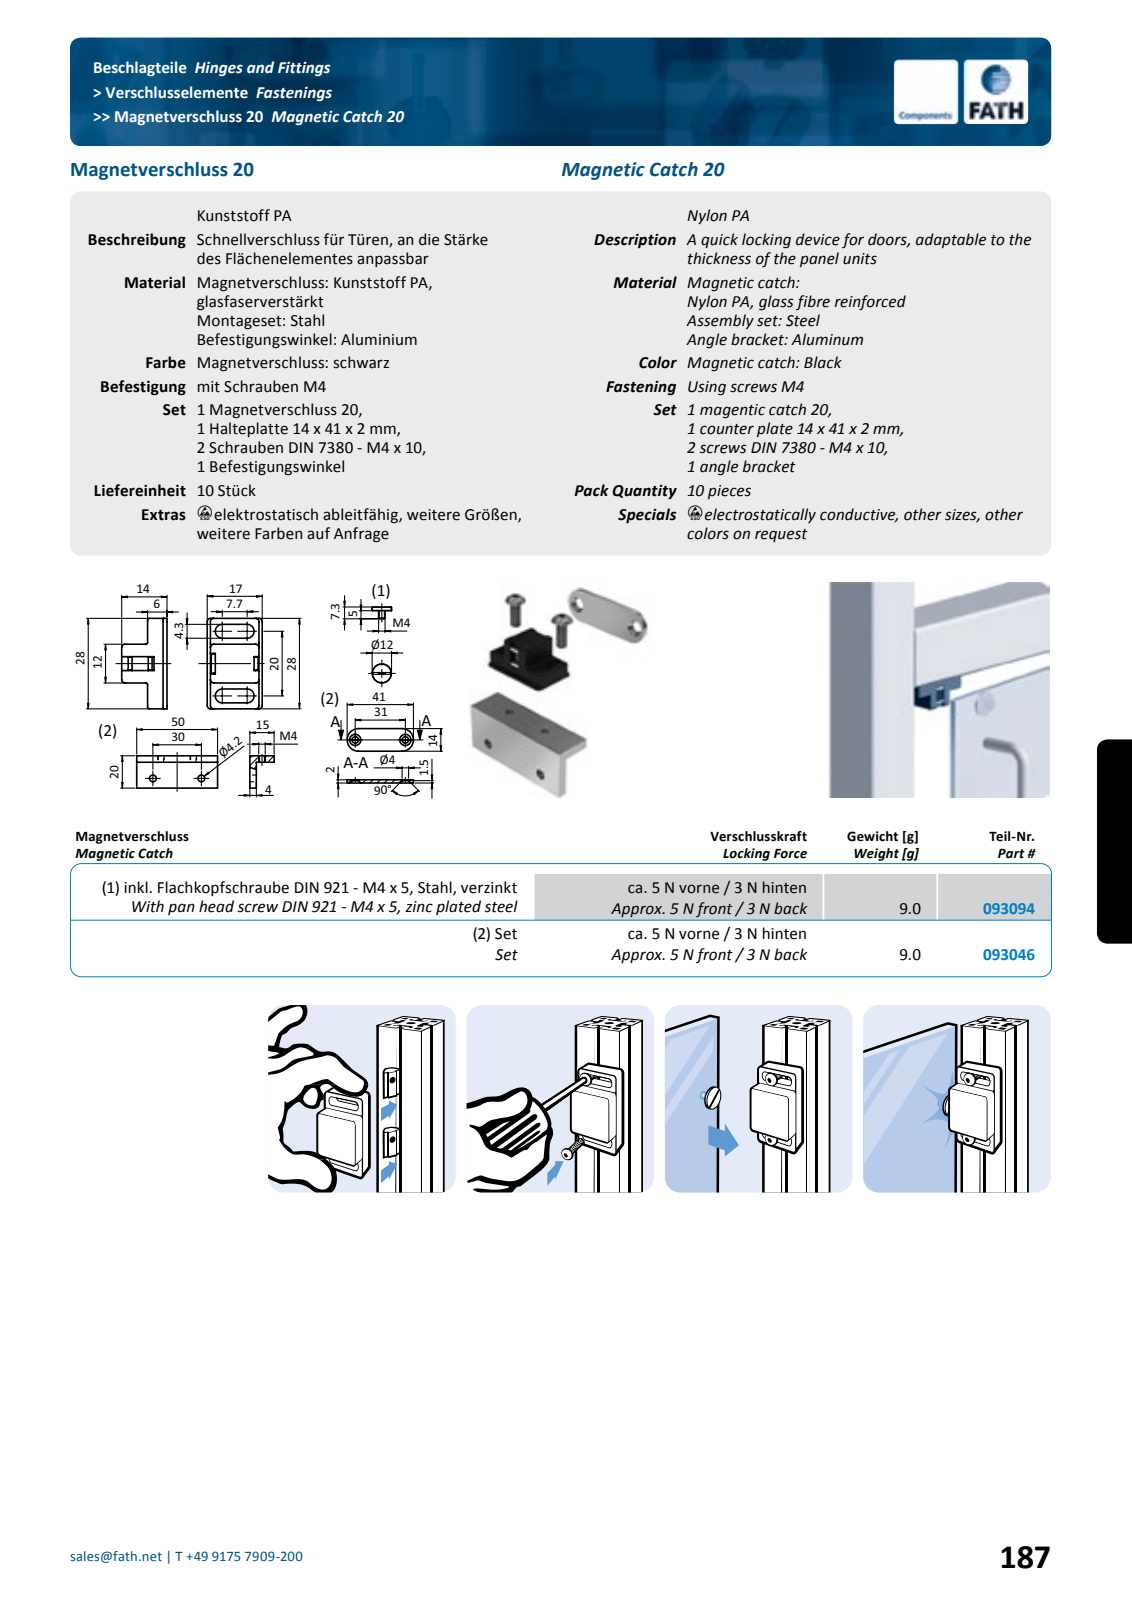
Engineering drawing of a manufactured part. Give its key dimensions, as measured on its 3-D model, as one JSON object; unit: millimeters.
{"part_name": "fath_093046_1; fath_093046_2; fath_093046_3; fath_093046_4 (+4 more)", "step_written_by": "Spatial InterOp 3D (automotive_design)", "units": "millimeters", "bodies": {"solids": 8, "faces": 221, "planar": 107, "cylindrical": 68, "other": 46}, "overall_size": [50, 35.3, 17.87], "volume_mm3": 9956, "surface_area_mm2": 8831, "round_holes": [[3.3, 2], [4, 2], [4.2, 2]], "round_bosses_or_shafts": [[7.6, 2], [4, 2]], "partial_cylinders_radius": [[1, 16], [0.2, 8], [0.5, 6], [2.15, 4], [7, 2]], "face_to_face_distances": [4, 2, 10, 17.87, 13.87, 16, 15.87, 11.87, 20, 15], "hole_center_spacings": [22.31, 37.78, 20, 30, 31]}
